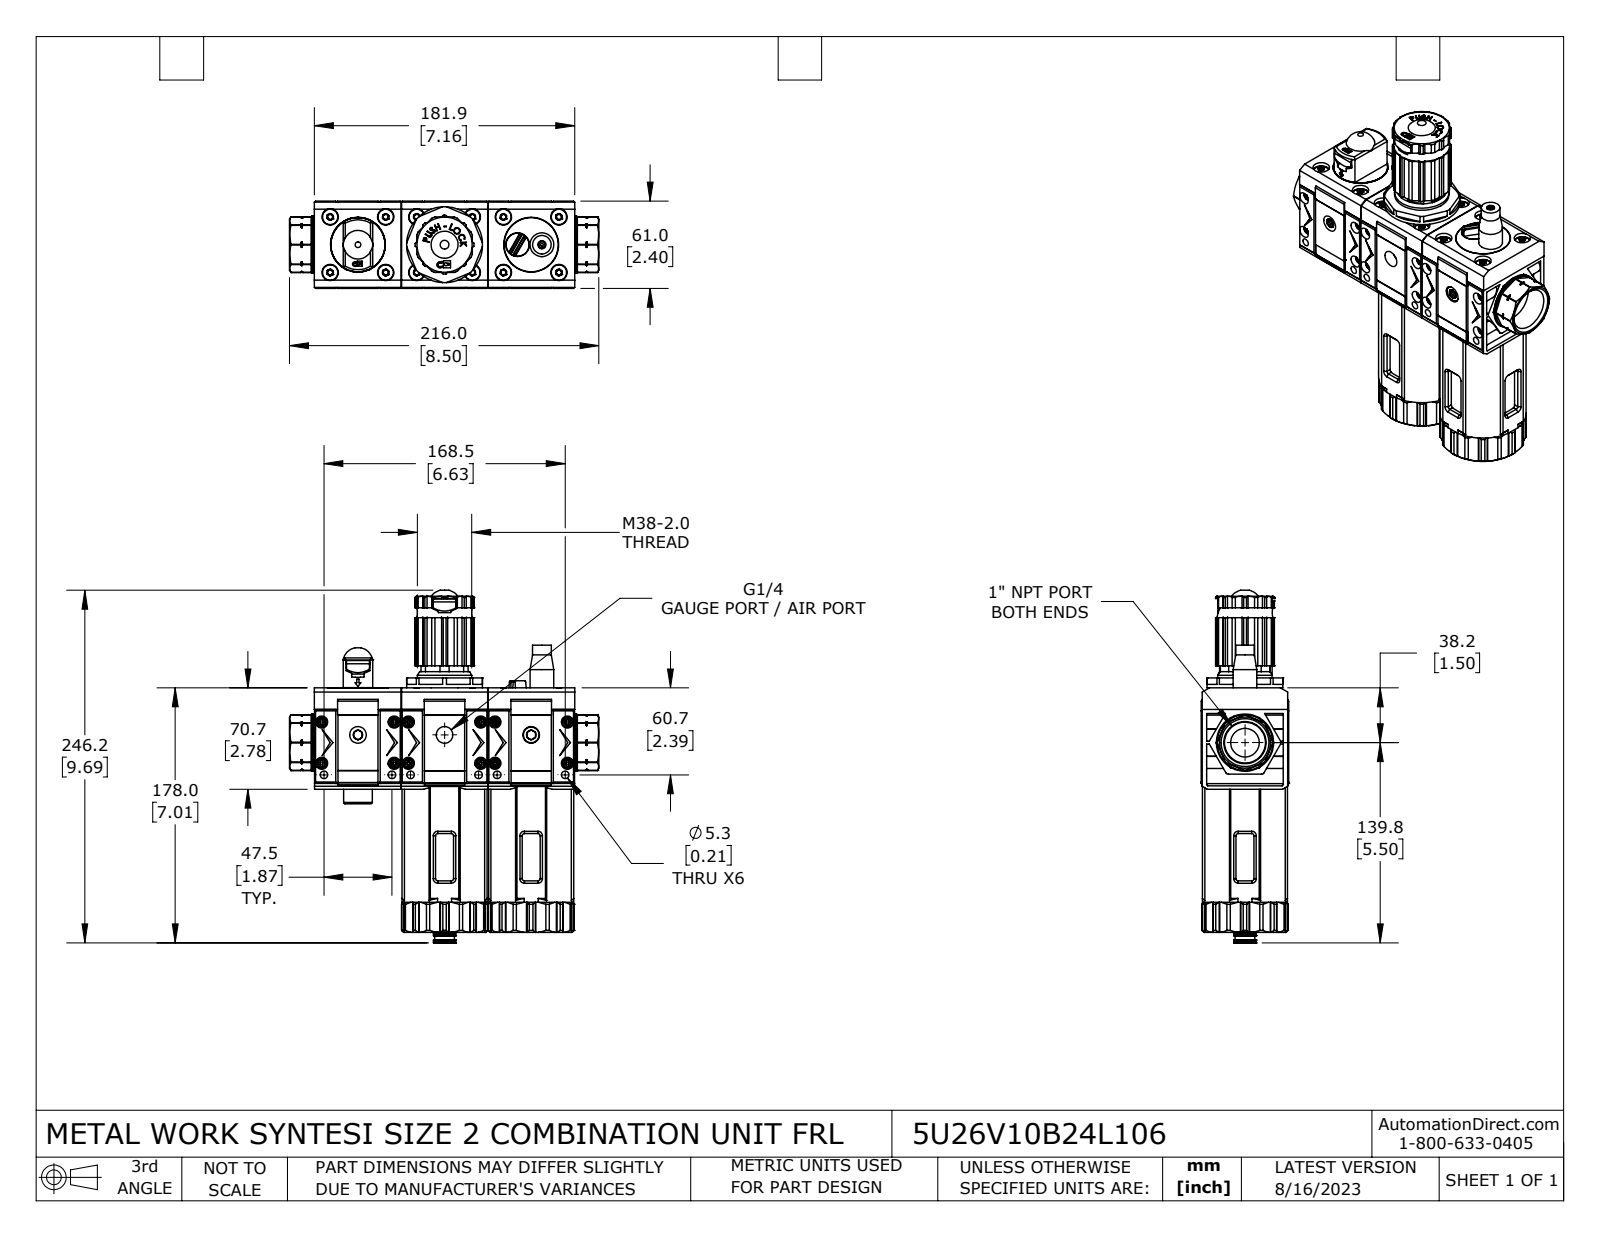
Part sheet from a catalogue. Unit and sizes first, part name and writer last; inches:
Units: inches
Overall size (bounding box): 9.693 × 8.504 × 2.402
Round holes (diameter × count): ⌀0.128 ×12, ⌀0.165 ×12, ⌀0.331 ×12, ⌀0.449 ×12, ⌀0.209 ×6, ⌀0.457 ×3, ⌀1.508 ×3, ⌀1.929 ×2, ⌀1.969 ×2, ⌀2.008 ×2, ⌀2.028 ×2, ⌀0.126 ×1
Round bosses / shafts (diameter × count): ⌀0.276 ×12, ⌀0.189 ×12, ⌀0.15 ×12, ⌀1.496 ×2, ⌀2.087 ×1, ⌀1.575 ×1, ⌀1.488 ×1, ⌀1.378 ×1
Partial cylindrical surfaces — rounded edges, fillets, slot ends (radius × count): R0.011 ×84, R0.02 ×32, R0.059 ×16, R0.069 ×12, R0.191 ×12, R0.242 ×6, R0.807 ×4, R0.12 ×3
Main face-to-face distances: 2.382, 2.39, 0.094, 2.193, 2.098, 2.402, 2.374, 3.11, 5.303, 3.205
Hole centre spacings: 2.382, 1.08, 1.528, 4.764, 1.789, 2.638, 2.83, 3.237
Volume: 68.95 in³ · Surface area: 514.9 in²
Bodies: 40 solids, 3920 faces (2219 planar, 1083 cylindrical, 618 other)
Part name (STEP PRODUCT): 5U26V10B24L106
STEP written by: SolidWorks 2021 (CONFIG_CONTROL_DESIGN)
